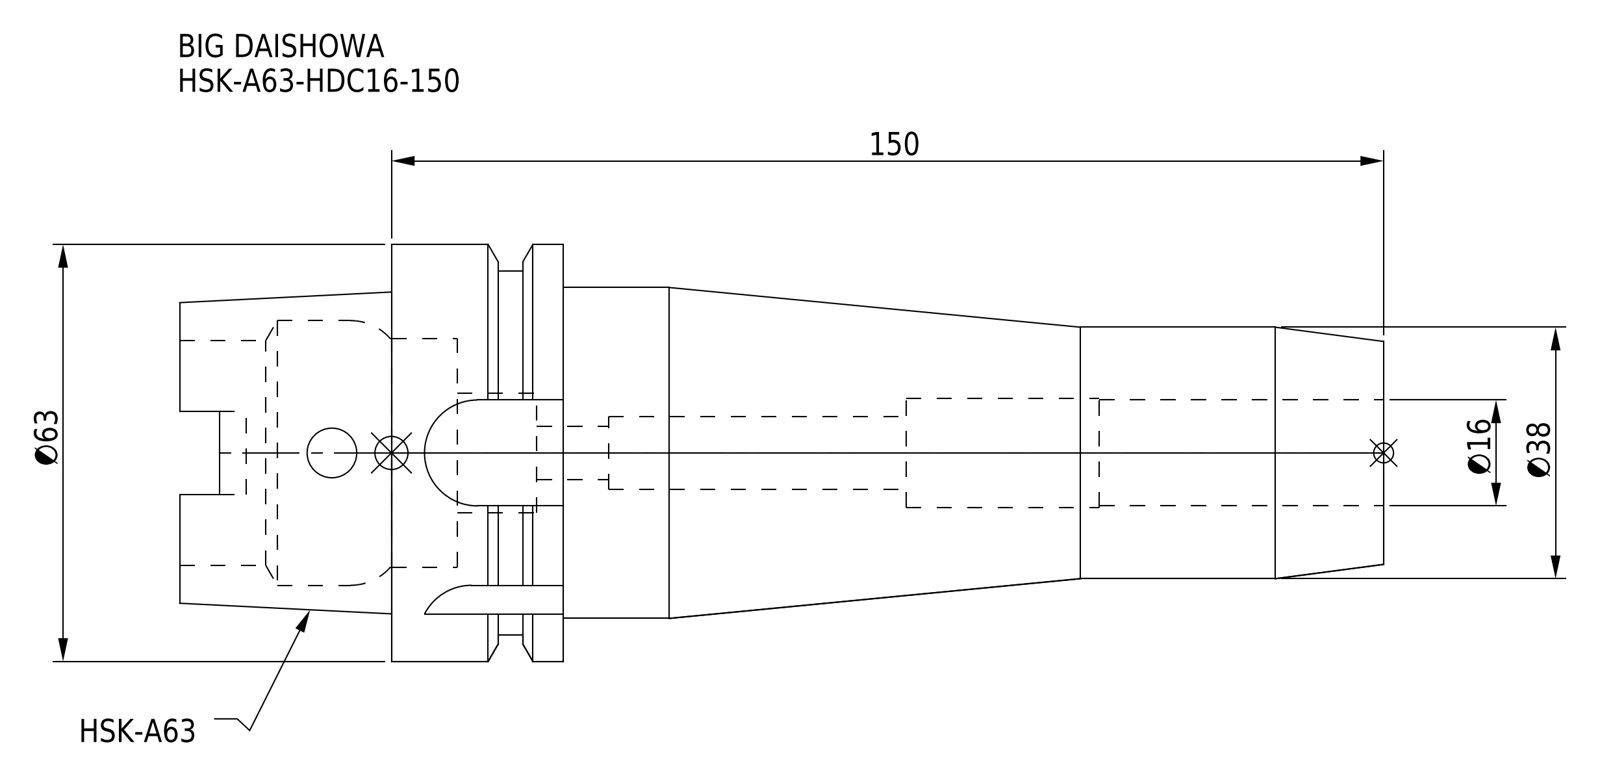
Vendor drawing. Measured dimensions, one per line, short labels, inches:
name: HSK-A63-HDC16-150
written by: CREO PARAMETRIC BY PTC INC, 2016380 (AUTOMOTIVE_DESIGN)
unit: in
bodies: 1 solid, 98 faces (39 planar, 41 cylindrical, 18 other)
size: 7.165 × 2.48 × 2.48
volume: 14.56 in³; area: 66.95 in²
holes: 1× ⌀0.295, 1× ⌀0.315, 1× ⌀0.433, 1× ⌀0.63, 1× ⌀0.65, 1× ⌀0.709, 1× ⌀1.339, 1× ⌀1.358, 1× ⌀1.575
bosses: 1× ⌀2.48, 1× ⌀2.165, 1× ⌀1.969, 1× ⌀1.496
rounds: 4× R0.113, 4× R0.315
face distances: 1.024, 4.882, 5.906, 5.514, 0.632, 0.392, 7.165, 2.283, 1.652, 1.26
